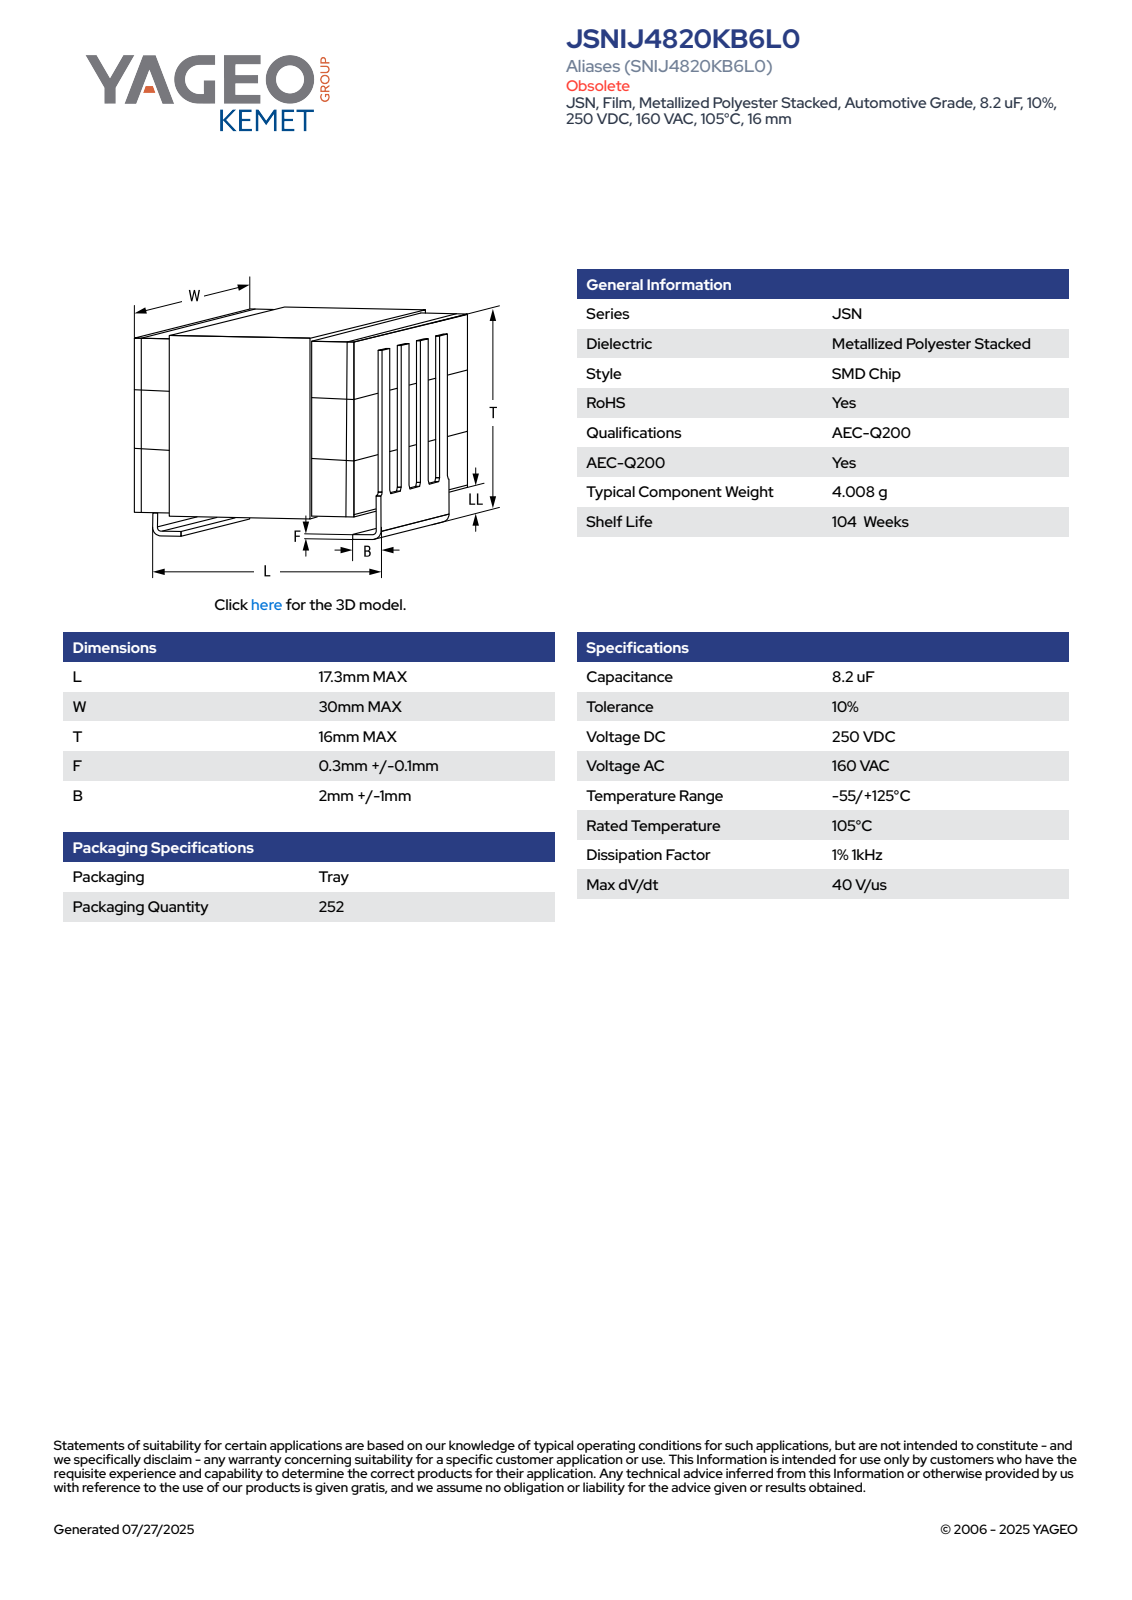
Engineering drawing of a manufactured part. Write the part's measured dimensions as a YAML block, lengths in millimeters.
part_name: "CFS_KJSN_L17.3W30T16F0.40"
step_written_by: "SolidWorks 2014 (AUTOMOTIVE_DESIGN)"
units: millimeters
bodies: {solids: 4, faces: 101, planar: 97, cylindrical: 4, other: 0}
overall_size: [30, 17.3, 16]
volume: 6545
surface_area: 3943
partial_cylinders:
  - {radius: 0.2, count: 4}
face_to_face_distances: [4.28, 8.62, 4.18, 8.52, 4.34, 0.4, 16.9, 4.38, 8.72, 12.9]
